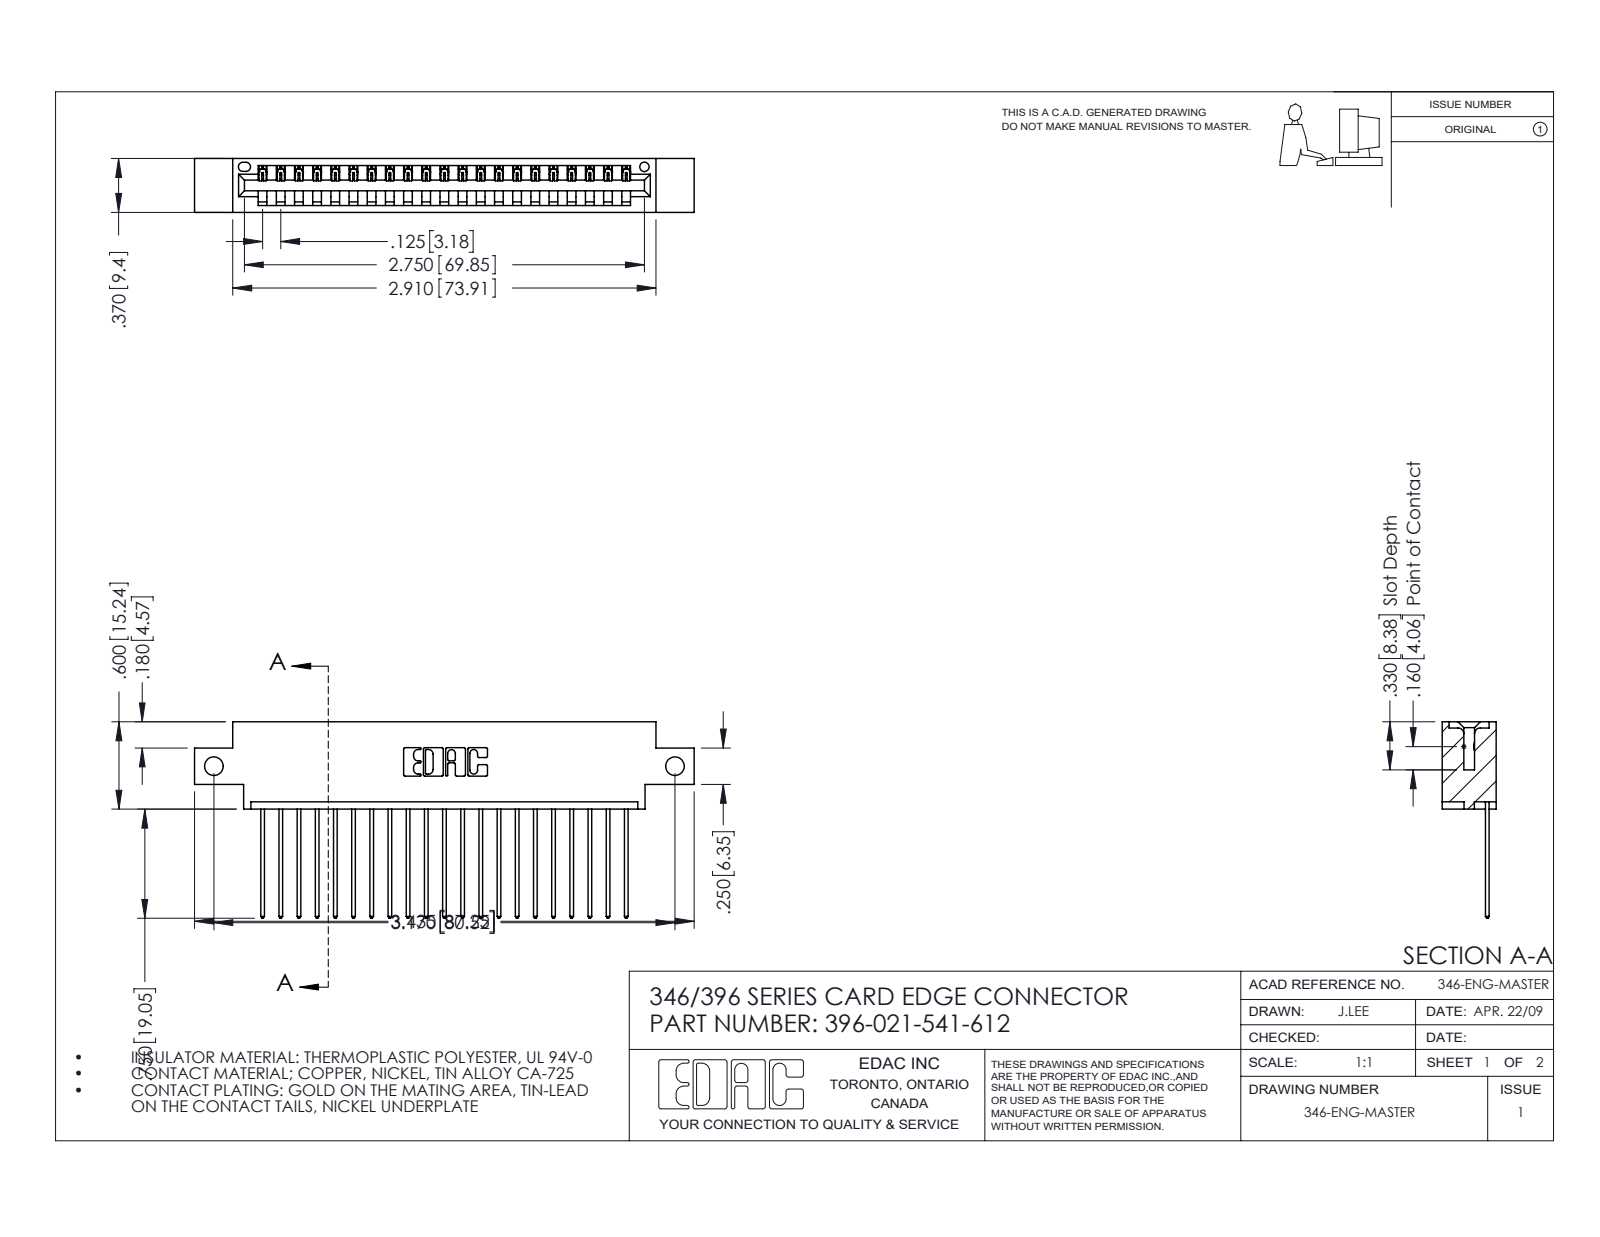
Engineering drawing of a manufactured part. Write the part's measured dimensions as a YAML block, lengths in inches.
part_name: "345-292-001_345-293-141; 346 Part_0.170 Offset - Side Mount; 396-021-541-612"
step_written_by: "SolidWorks 2016 (CONFIG_CONTROL_DESIGN)"
units: inches
bodies: {solids: 22, faces: 1344, planar: 920, cylindrical: 424, other: 0}
overall_size: [3.435, 1.35, 0.37]
volume: 0.49
surface_area: 15.88
round_holes:
  - {diameter: 0.128, count: 2}
  - {diameter: 0.064, count: 1}
partial_cylinders:
  - {radius: 0.006, count: 42}
  - {radius: 0.01, count: 42}
  - {radius: 0.01, count: 22}
  - {radius: 0.007, count: 6}
  - {radius: 0.031, count: 6}
  - {radius: 0.026, count: 3}
  - {radius: 0.031, count: 2}
  - {radius: 0.04, count: 2}
face_to_face_distances: [0.048, 0.322, 0.37, 0.25, 0.072, 0.298, 0.025, 0.148, 0.222, 0.1]
hole_center_spacings: [3.17]
